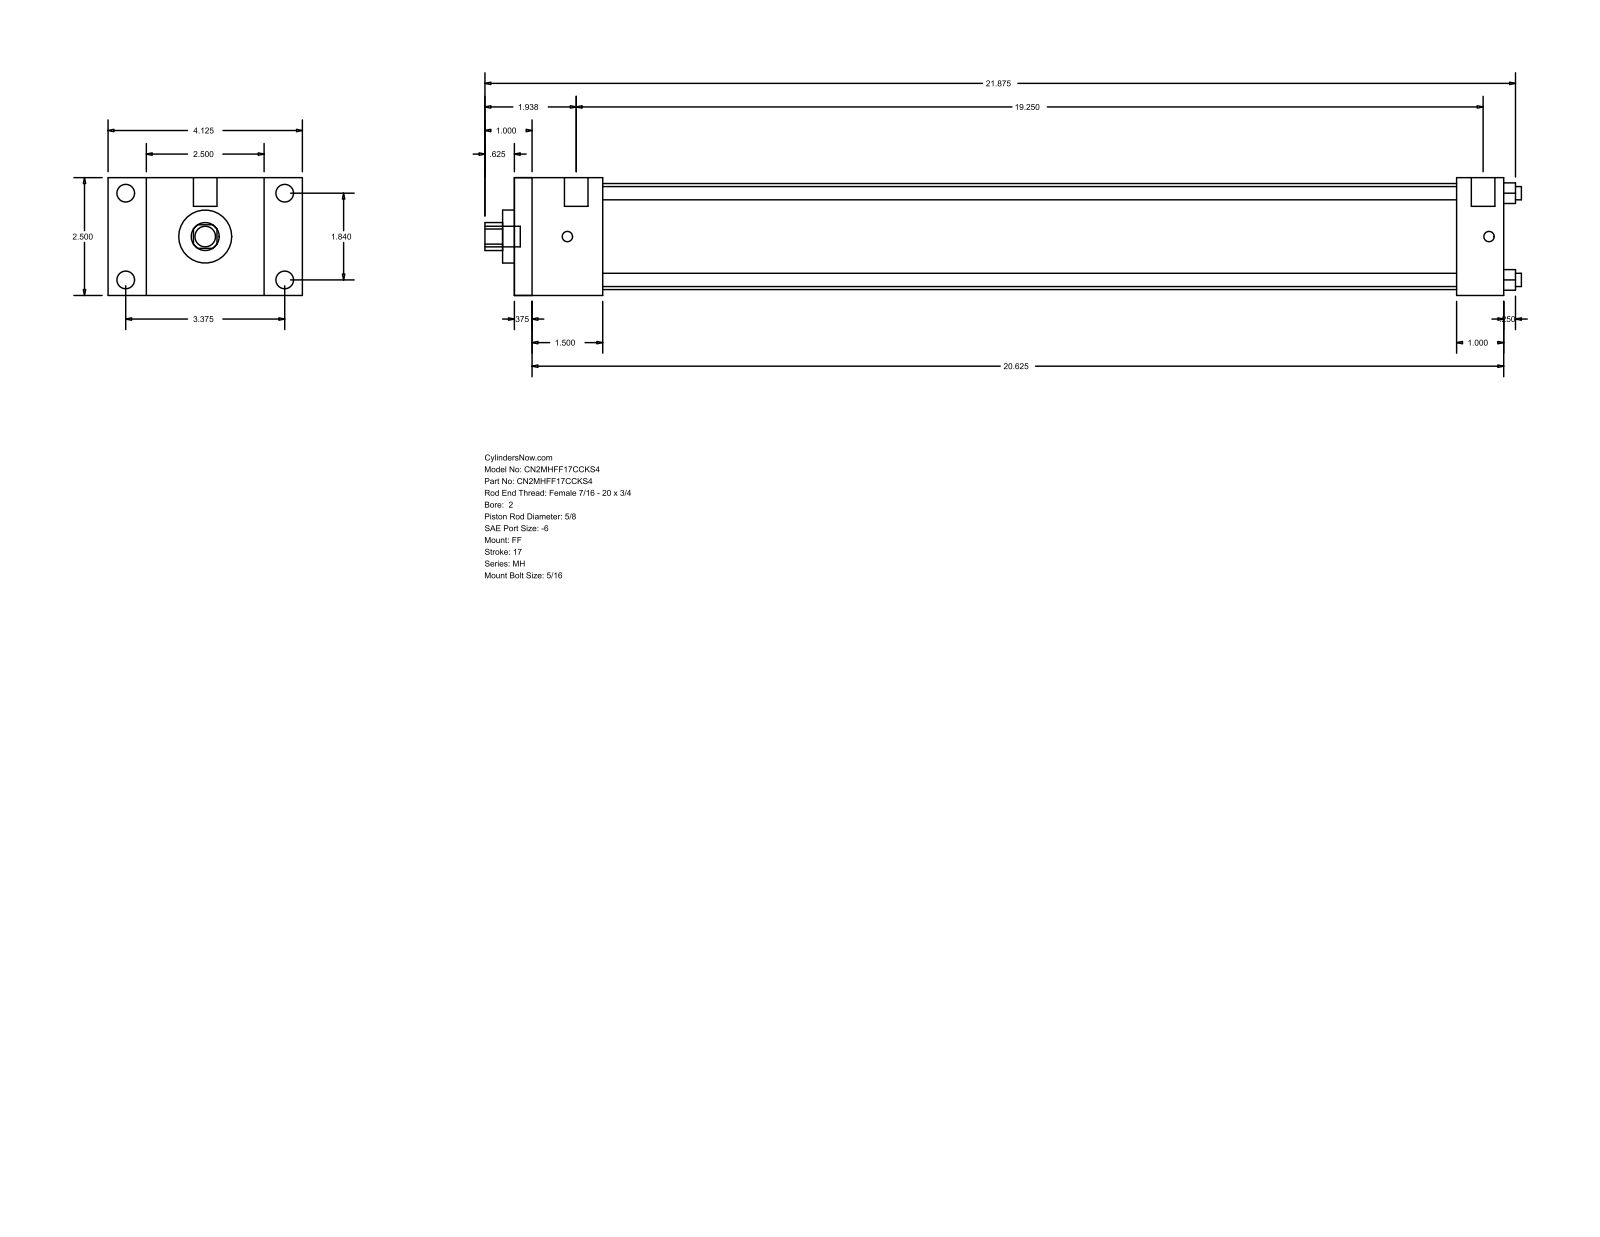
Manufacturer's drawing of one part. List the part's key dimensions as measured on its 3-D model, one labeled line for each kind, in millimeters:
Part name (STEP PRODUCT): MH_FF__0200_0.625
STEP written by: GSSL Pune (CONFIG_CONTROL_DESIGN)
Units: millimetres
Bodies: 0 solids, 92 faces (64 planar, 28 cylindrical, 0 other)
Overall size (bounding box): 558.8 × 104.78 × 63.5
Round holes (diameter × count): ⌀7.14 ×4, ⌀15.88 ×1, ⌀28.57 ×1, ⌀57.15 ×1
Round bosses / shafts (diameter × count): ⌀9.53 ×4, ⌀5.56 ×4, ⌀12.7 ×2, ⌀11.11 ×1
Partial cylindrical surfaces — rounded edges, fillets, slot ends (radius × count): R7.54 ×1
Main face-to-face distances: 63.5, 533.39, 9.52, 523.87, 38.1, 47.62, 508, 498.48, 460.38, 485.77
Hole centre spacings: 33.05, 46.74, 66.1
